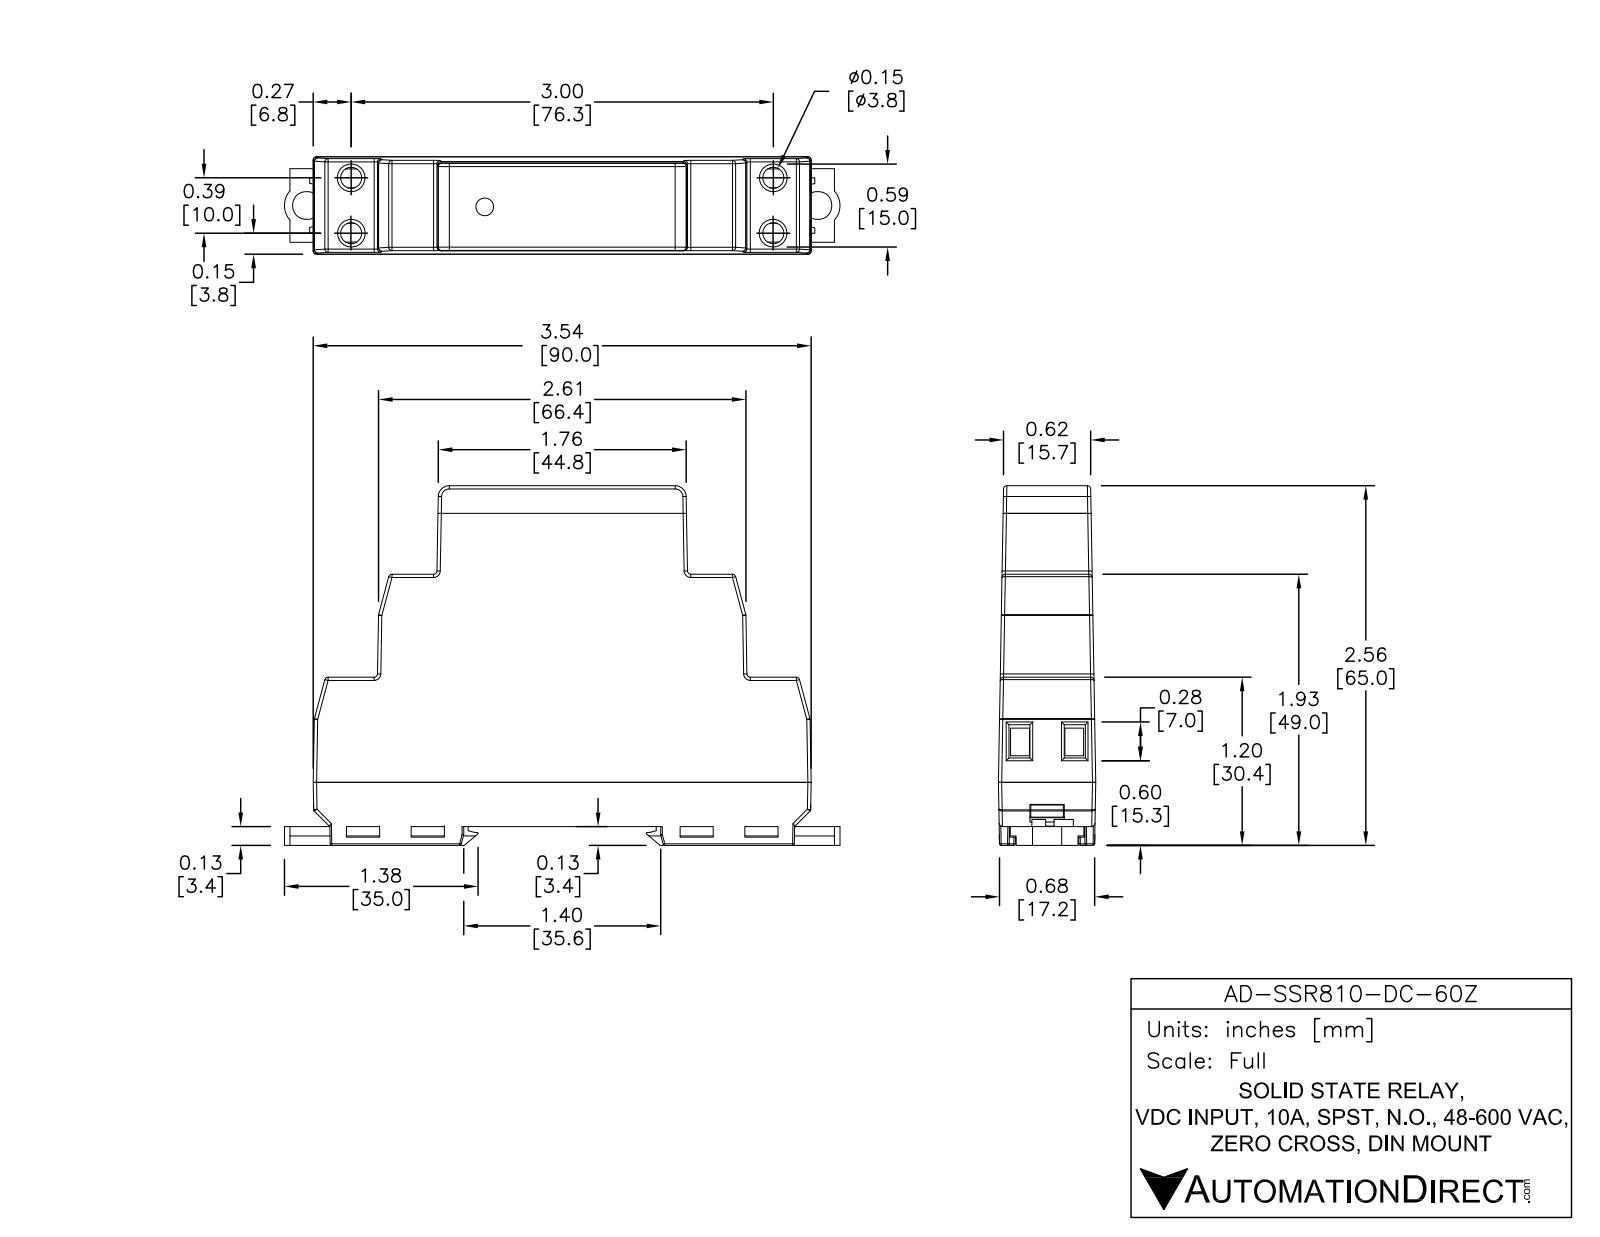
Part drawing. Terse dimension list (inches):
name: AD-SSR810-DC-60Z
written by: SolidWorks 2013 (AUTOMOTIVE_DESIGN)
unit: in
bodies: 1 solid, 833 faces (486 planar, 78 cylindrical, 269 other)
size: 3.924 × 2.616 × 0.685
volume: 4.605 in³; area: 24.23 in²
holes: 4× ⌀0.19, 2× ⌀0.2
bosses: 1× ⌀0.105
rounds: 41× R0.015, 2× R0.06, 2× R0.172
face distances: 2.525, 0.049, 2.574, 0.425, 2.215, 0.025, 0.05, 1.934, 1.885, 0.64
hole spacings: 0.338, 3.3, 0.364, 3.01, 3.032, 3.58
